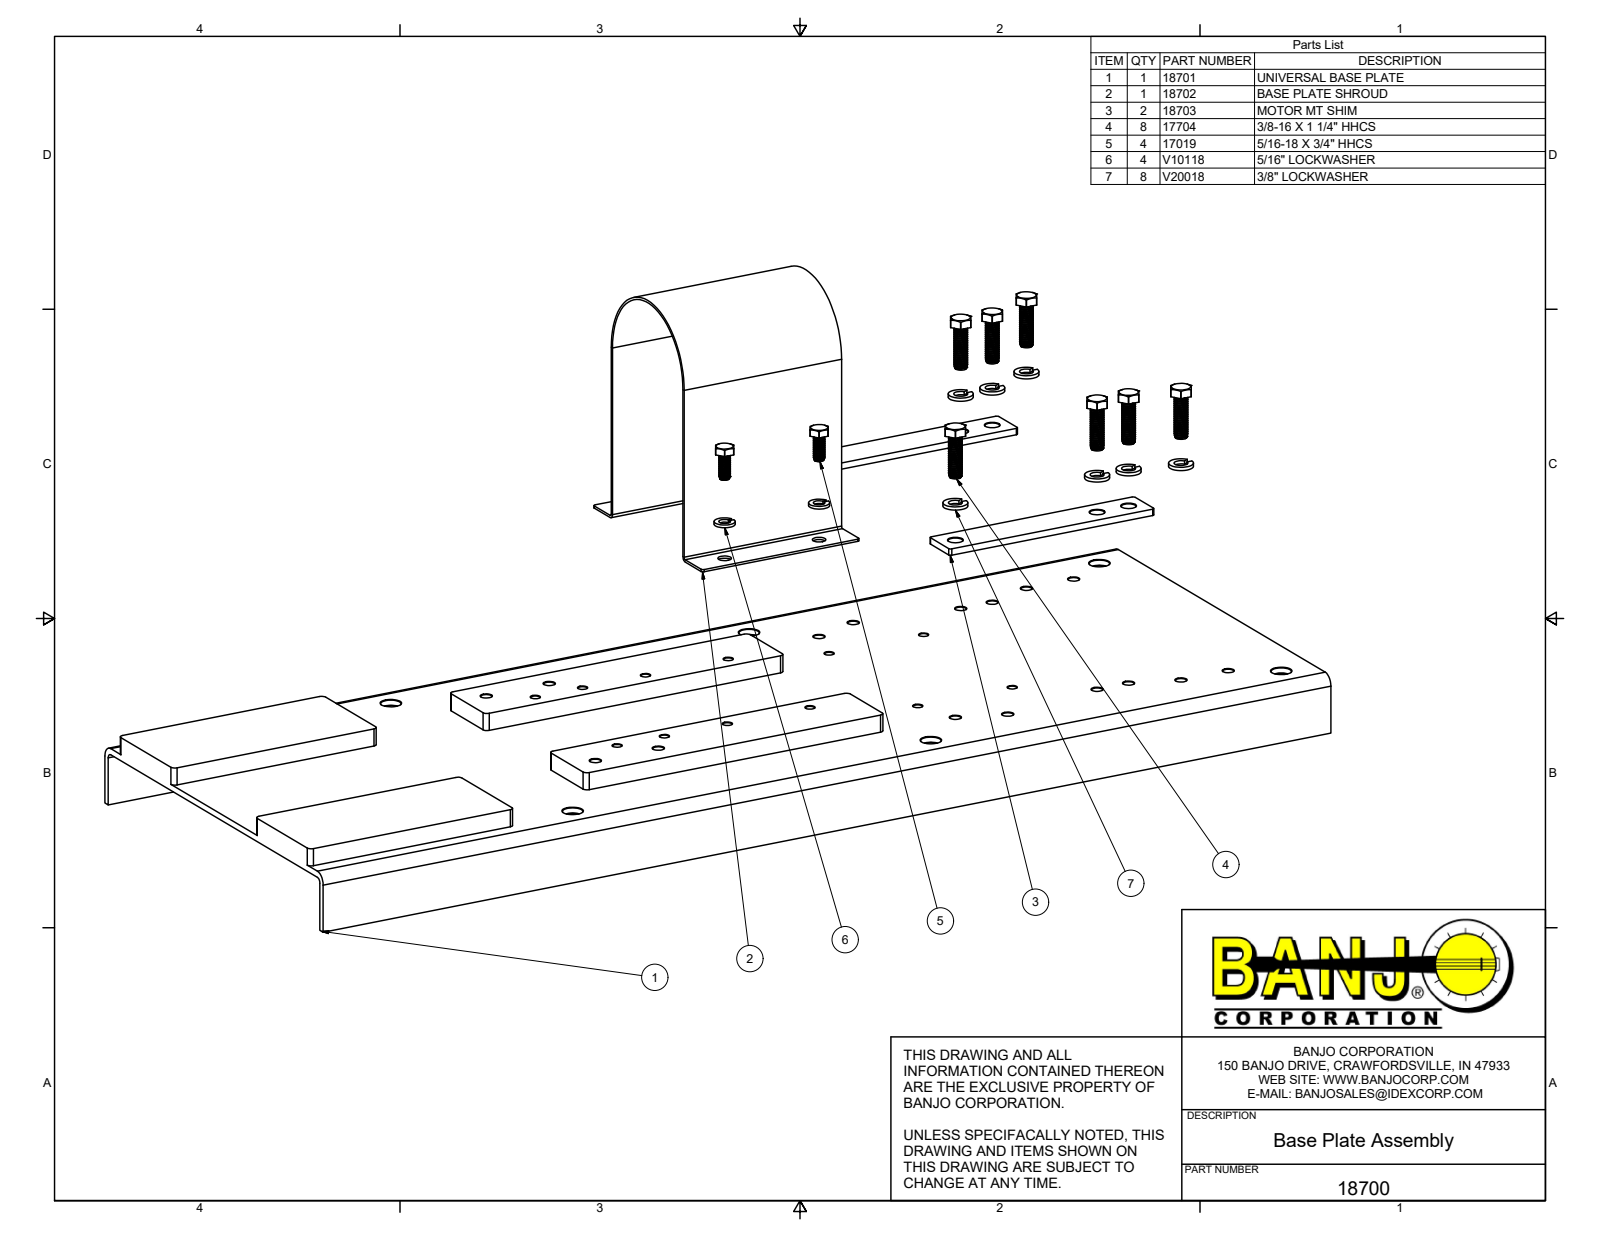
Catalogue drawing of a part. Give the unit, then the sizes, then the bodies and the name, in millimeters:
Units: millimetres
Overall size (bounding box): 812.8 × 304.8 × 233.43
Round holes (diameter × count): ⌀7.8 ×16, ⌀6.4 ×12, ⌀9.78 ×8, ⌀10.32 ×6, ⌀14.29 ×6, ⌀8.18 ×4, ⌀9.52 ×4
Round bosses / shafts (diameter × count): ⌀8.24 ×152, ⌀6.82 ×52, ⌀17.46 ×8, ⌀9.52 ×8, ⌀14.81 ×4, ⌀7.94 ×4
Partial cylindrical surfaces — rounded edges, fillets, slot ends (radius × count): R3.17 ×26, R4.12 ×16, R1.52 ×12, R8.18 ×8, R3.41 ×4, R7.27 ×4, R1.47 ×2, R3.38 ×2
Main face-to-face distances: 4.55, 12.7, 17.25, 300.25, 1.65, 29.95, 100.07, 304.8, 295.7, 109.54
Hole centre spacings: 114.3, 37.17, 139.7, 190.83, 206.18, 38.1, 50.8, 69.35
Volume: 2 663 000 mm³ · Surface area: 840 072 mm²
Bodies: 28 solids, 2304 faces (218 planar, 1058 cylindrical, 1028 other)
Part name (STEP PRODUCT): 18700; 18701; 18702; 18703 (+4 more)
STEP written by: Autodesk Inventor 2017 (AUTOMOTIVE_DESIGN)
